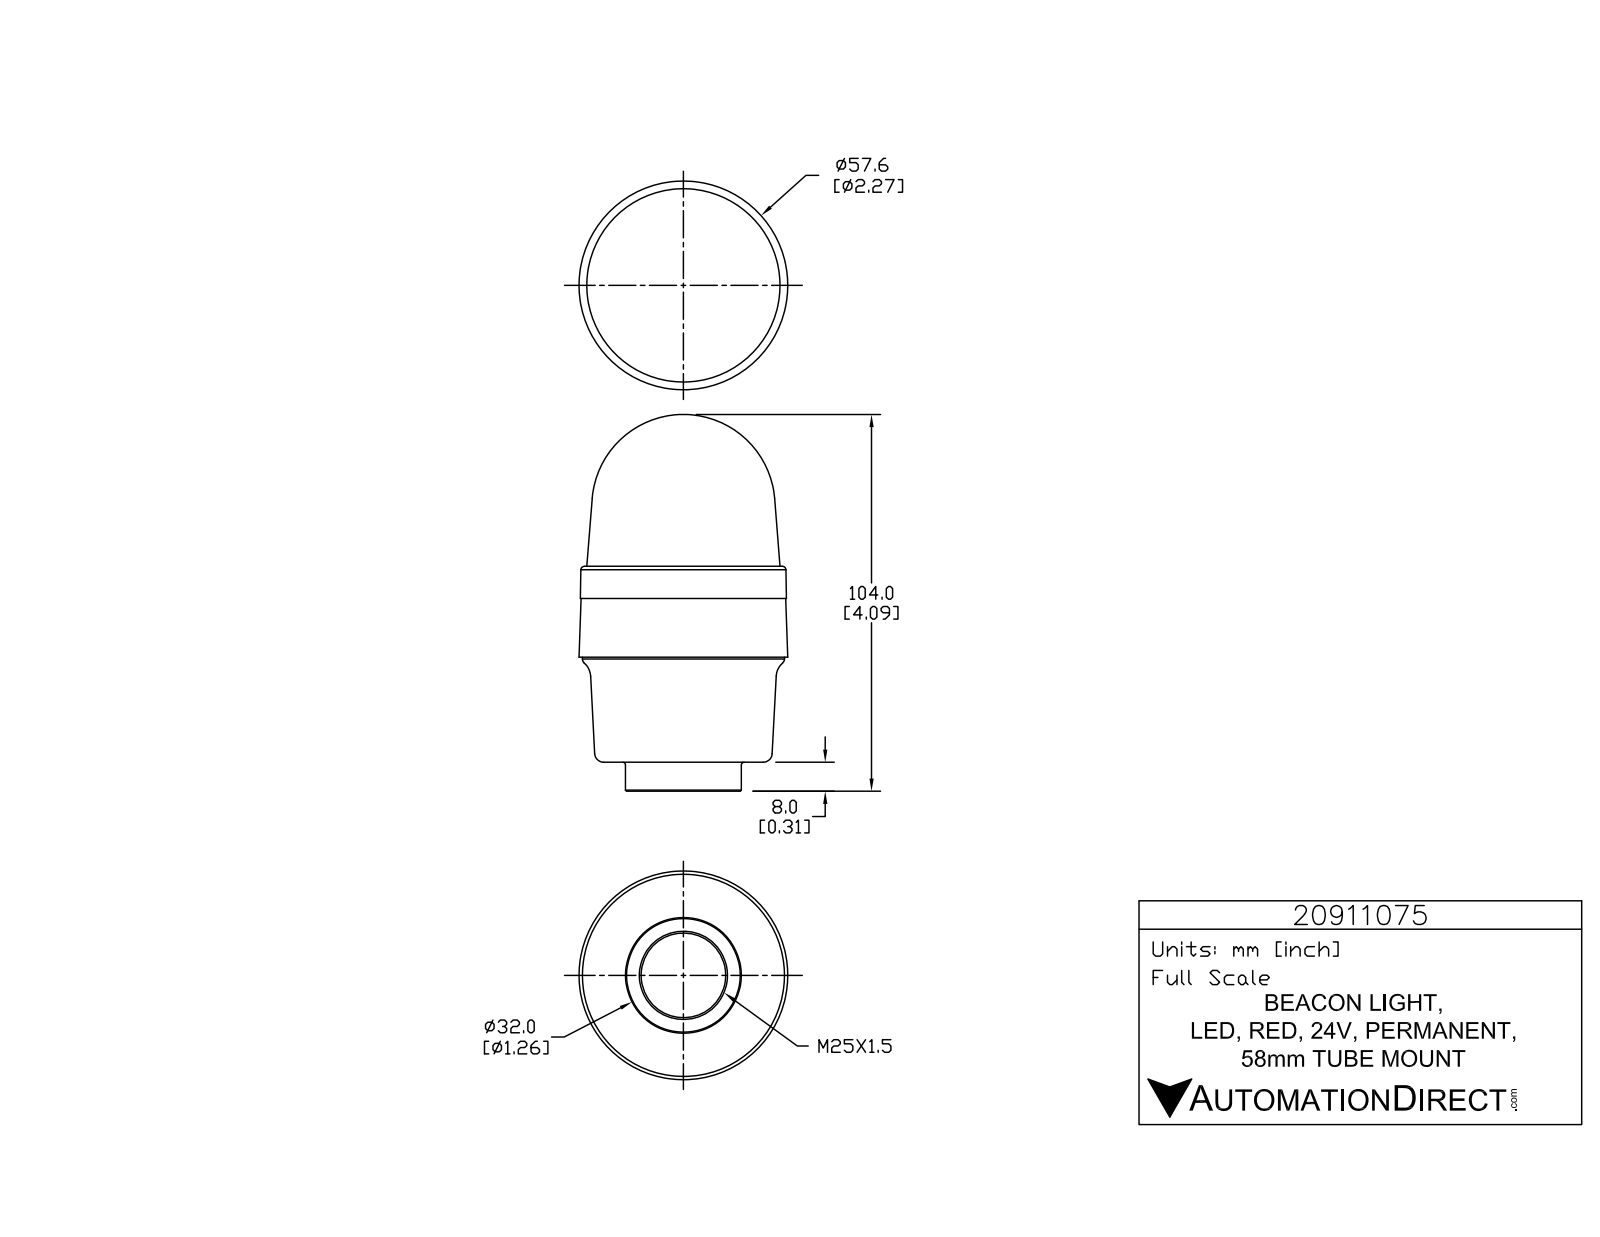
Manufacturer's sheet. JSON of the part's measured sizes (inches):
{"part_name": "20911075", "step_written_by": "SolidWorks 2015 (AUTOMOTIVE_DESIGN)", "units": "inches", "bodies": {"solids": 1, "faces": 791, "planar": 525, "cylindrical": 168, "other": 98}, "overall_size": [4.051, 2.269, 2.269], "volume_in3": 11.72, "surface_area_in2": 29.93, "round_holes": [[0.039, 3], [0.92, 1]], "round_bosses_or_shafts": [[0.226, 3], [0.056, 3], [2.197, 1], [1.26, 1]], "partial_cylinders_radius": [[0.008, 6], [0.008, 6], [0.008, 6], [0.131, 6], [0.004, 3], [0.005, 3], [0.008, 3], [0.008, 3]], "face_to_face_distances": [0.315, 1.142, 1.457, 0.988, 2.13, 2.445, 0.35, 0.638, 1.78, 2.094]}
